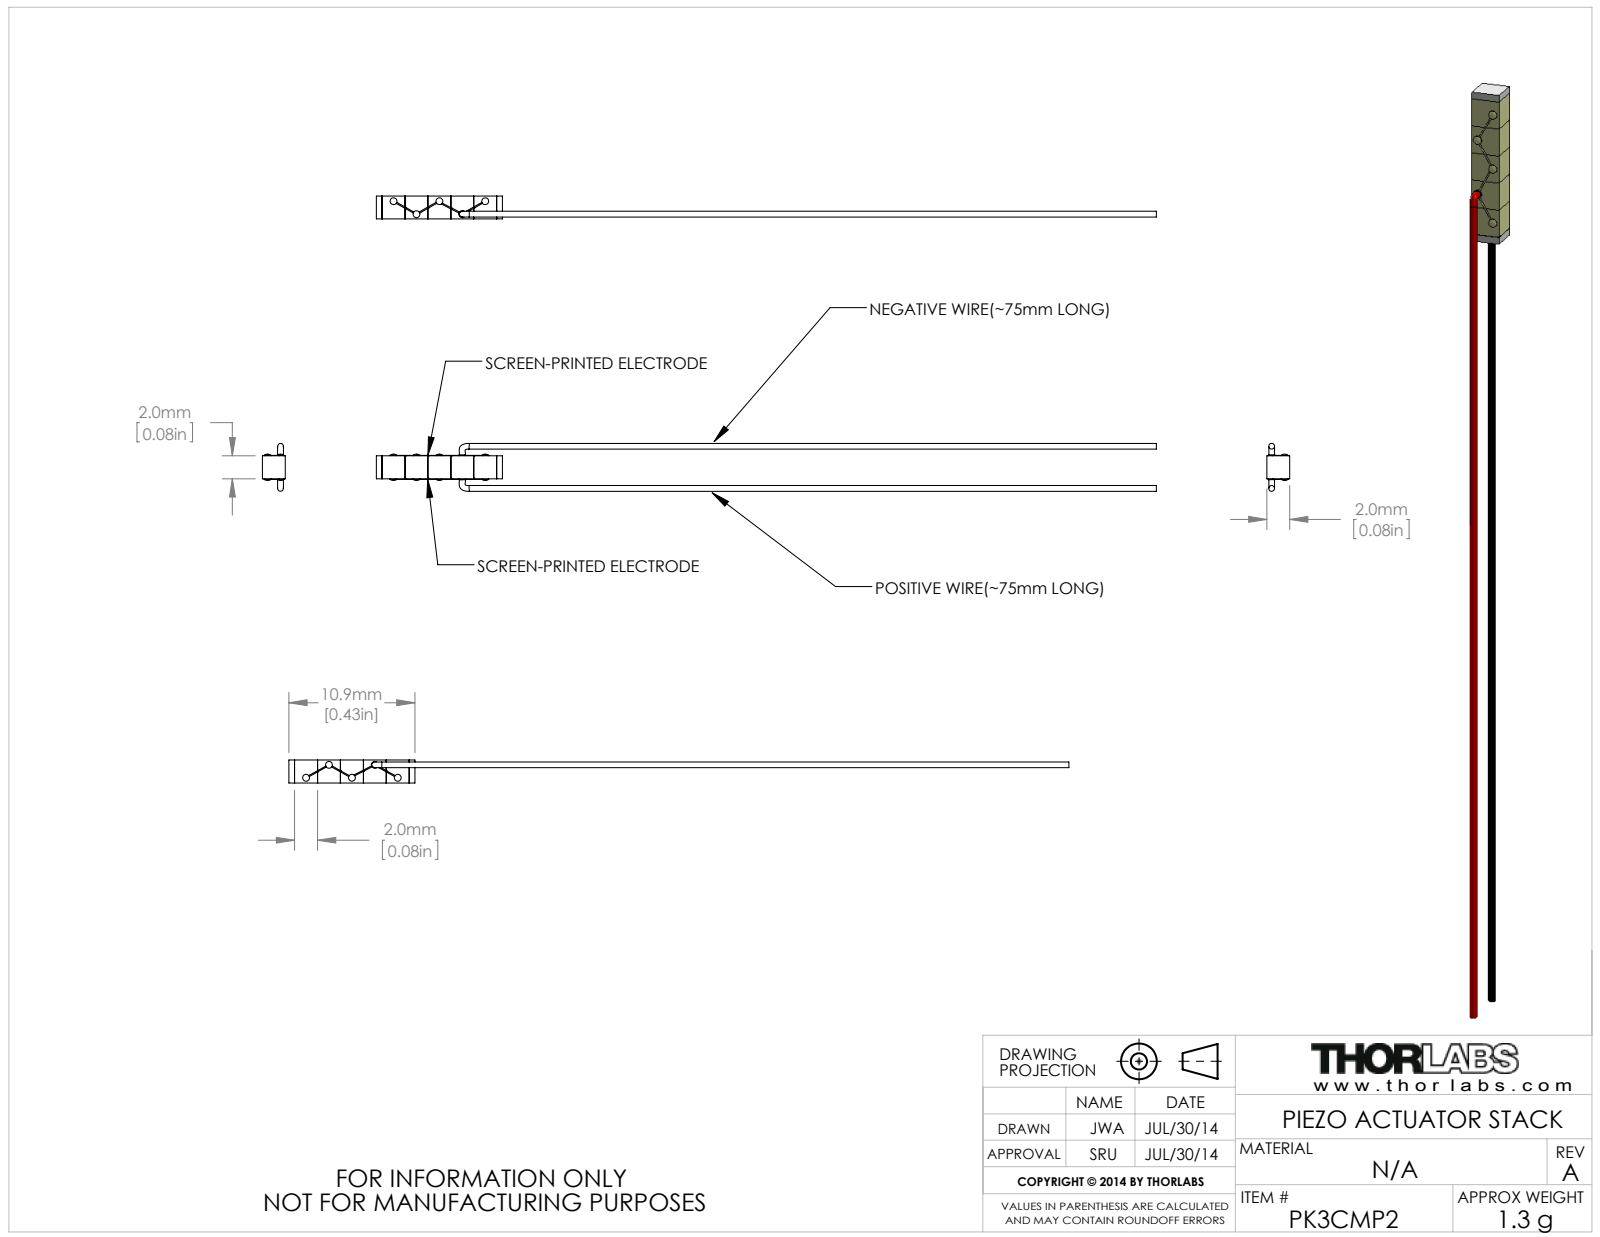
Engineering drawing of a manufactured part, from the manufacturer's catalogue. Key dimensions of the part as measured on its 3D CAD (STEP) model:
Part name (STEP PRODUCT): PK3CMP2
STEP written by: SolidWorks 2012 (AUTOMOTIVE_DESIGN)
Units: millimetres
Bodies: 3 solids, 124 faces (50 planar, 46 cylindrical, 28 other)
Overall size (bounding box): 68.1 × 4.18 × 2
Volume: 69 mm³ · Surface area: 339 mm²
Round bosses / shafts (diameter × count): ⌀0.6 ×5
Main face-to-face distances: 2, 4, 6, 8, 0.5, 10.51, 2.51, 4.51, 6.51, 8.51
